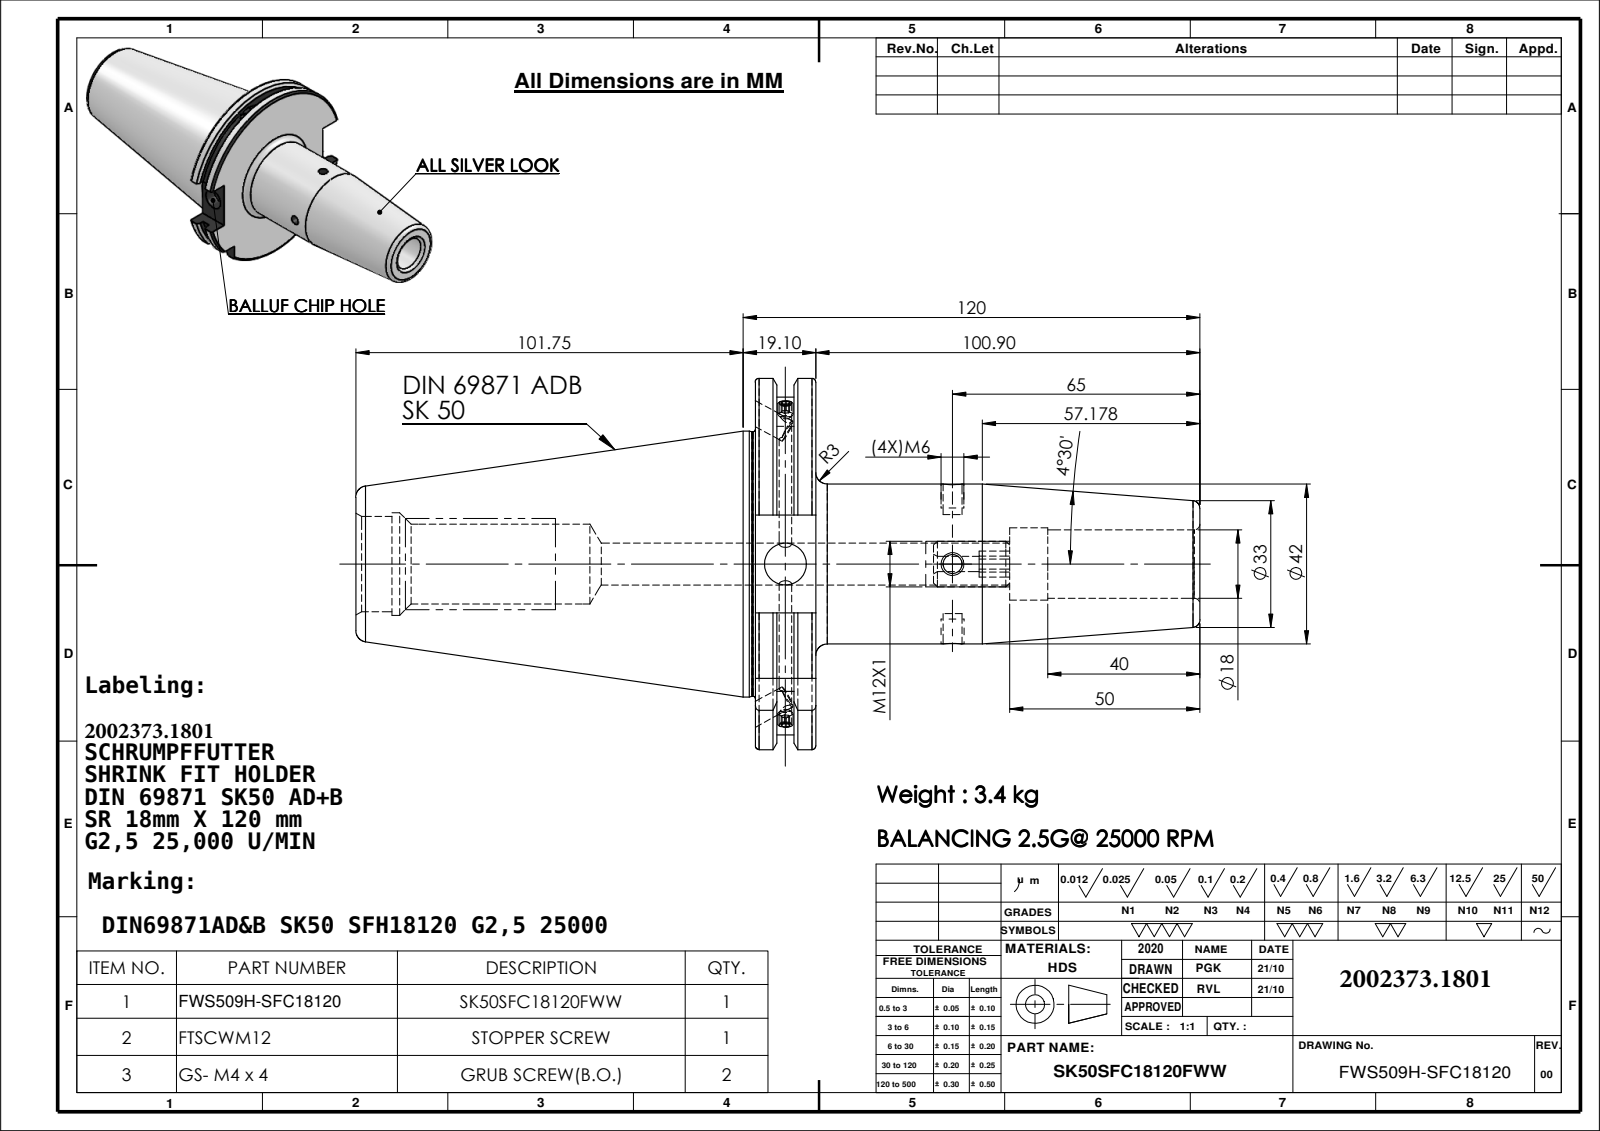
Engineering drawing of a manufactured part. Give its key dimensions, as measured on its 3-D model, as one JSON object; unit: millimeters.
{"part_name": "91506-SR218120", "step_written_by": "SolidWorks 2018 (AUTOMOTIVE_DESIGN)", "units": "millimeters", "bodies": {"solids": 1, "faces": 122, "planar": 29, "cylindrical": 53, "other": 40}, "overall_size": [221.75, 97.5, 94.05], "volume_mm3": 437926, "surface_area_mm2": 60396, "round_holes": [[5, 2], [6, 2], [11, 2], [3.3, 1], [17.99, 1], [19, 1], [21, 1], [25, 1], [27, 1]], "round_bosses_or_shafts": [[69.85, 1], [69.45, 1], [42, 1]], "partial_cylinders_radius": [[44.9, 1], [48.75, 1]], "face_to_face_distances": [15.9, 5.66, 10.24, 10.14, 4.48, 5.76, 104.95, 110.61, 115.09, 120.85], "hole_center_spacings": [43.9]}
